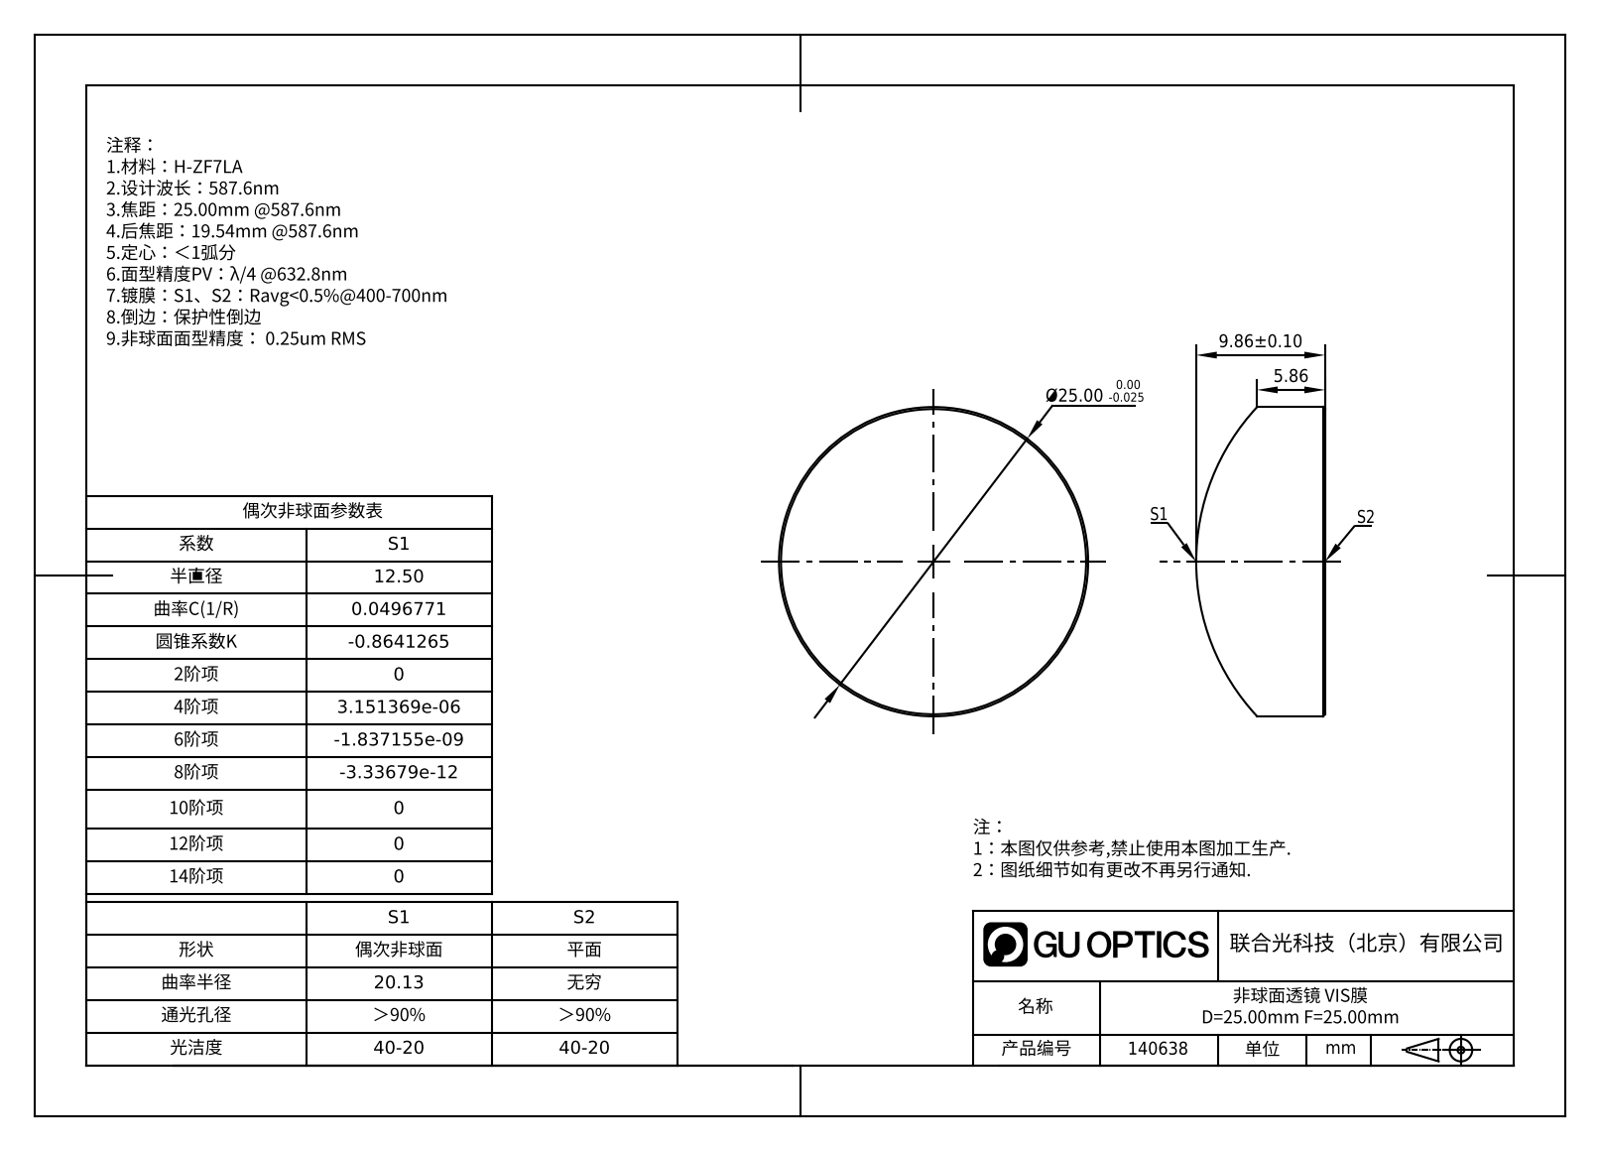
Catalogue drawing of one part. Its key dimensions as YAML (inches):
part_name: "GLA11-025-025-H-VIS"
step_written_by: "SolidWorks 2022 (AUTOMOTIVE_DESIGN)"
units: inches
bodies: {solids: 1, faces: 7, planar: 1, cylindrical: 2, other: 4}
overall_size: [0.984, 0.984, 0.388]
volume: 0.237
surface_area: 2.299
round_bosses_or_shafts:
  - {diameter: 0.984, count: 1}
